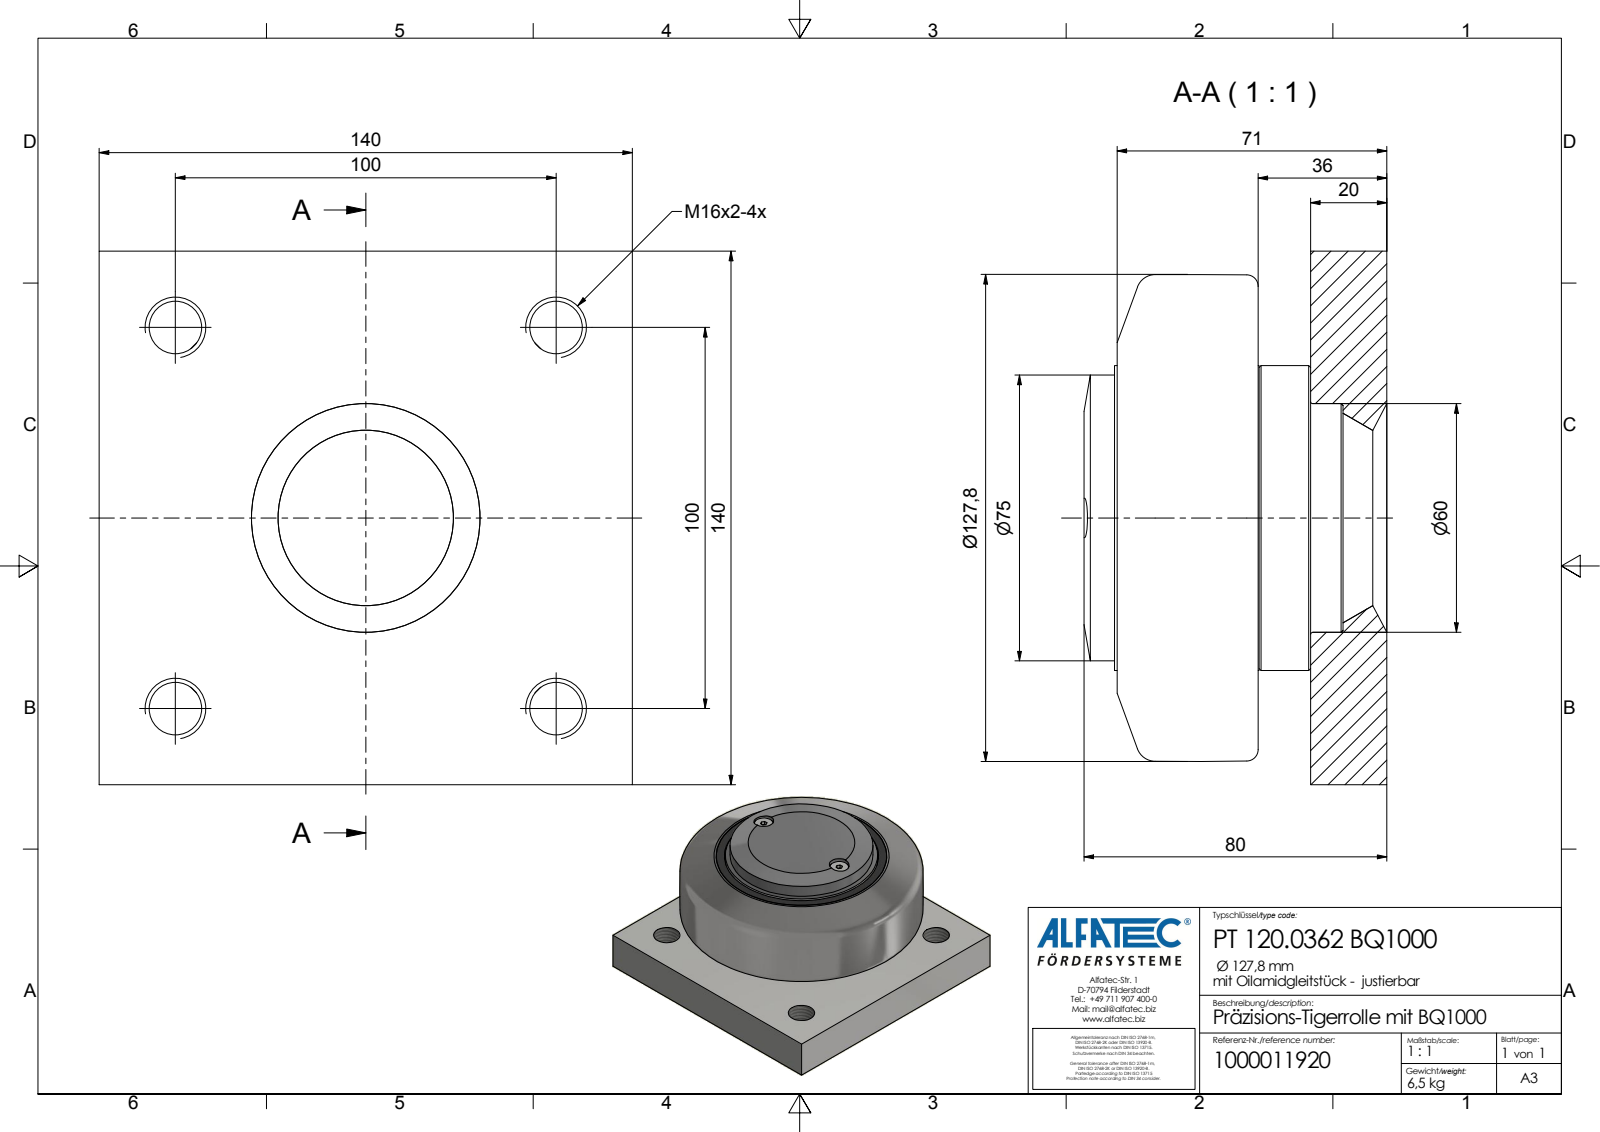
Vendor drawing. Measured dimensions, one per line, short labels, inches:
name: PT 120.0362 BQ1000_Kontur
written by: Autodesk Inventor 2020 (AUTOMOTIVE_DESIGN)
unit: in
bodies: 2 solids, 71 faces (36 planar, 24 cylindrical, 11 other)
size: 5.512 × 5.512 × 3.13
volume: 53.04 in³; area: 171.6 in²
holes: 4× ⌀0.545, 2× ⌀0.409, 1× ⌀0.118, 1× ⌀3.189, 1× ⌀3.425, 1× ⌀3.524, 1× ⌀3.74
bosses: 2× ⌀0.384, 1× ⌀3.417, 1× ⌀3.327, 1× ⌀3.15, 1× ⌀3.11, 1× ⌀2.953
rounds: 1× R1.398
face distances: 0.787, 5.512, 1.331, 0.543, 3.13, 2.343, 1.799, 0.256, 1.201, 0.146
hole spacings: 2.151, 2.784, 3.648, 3.937, 1.102, 5.568, 2.205
